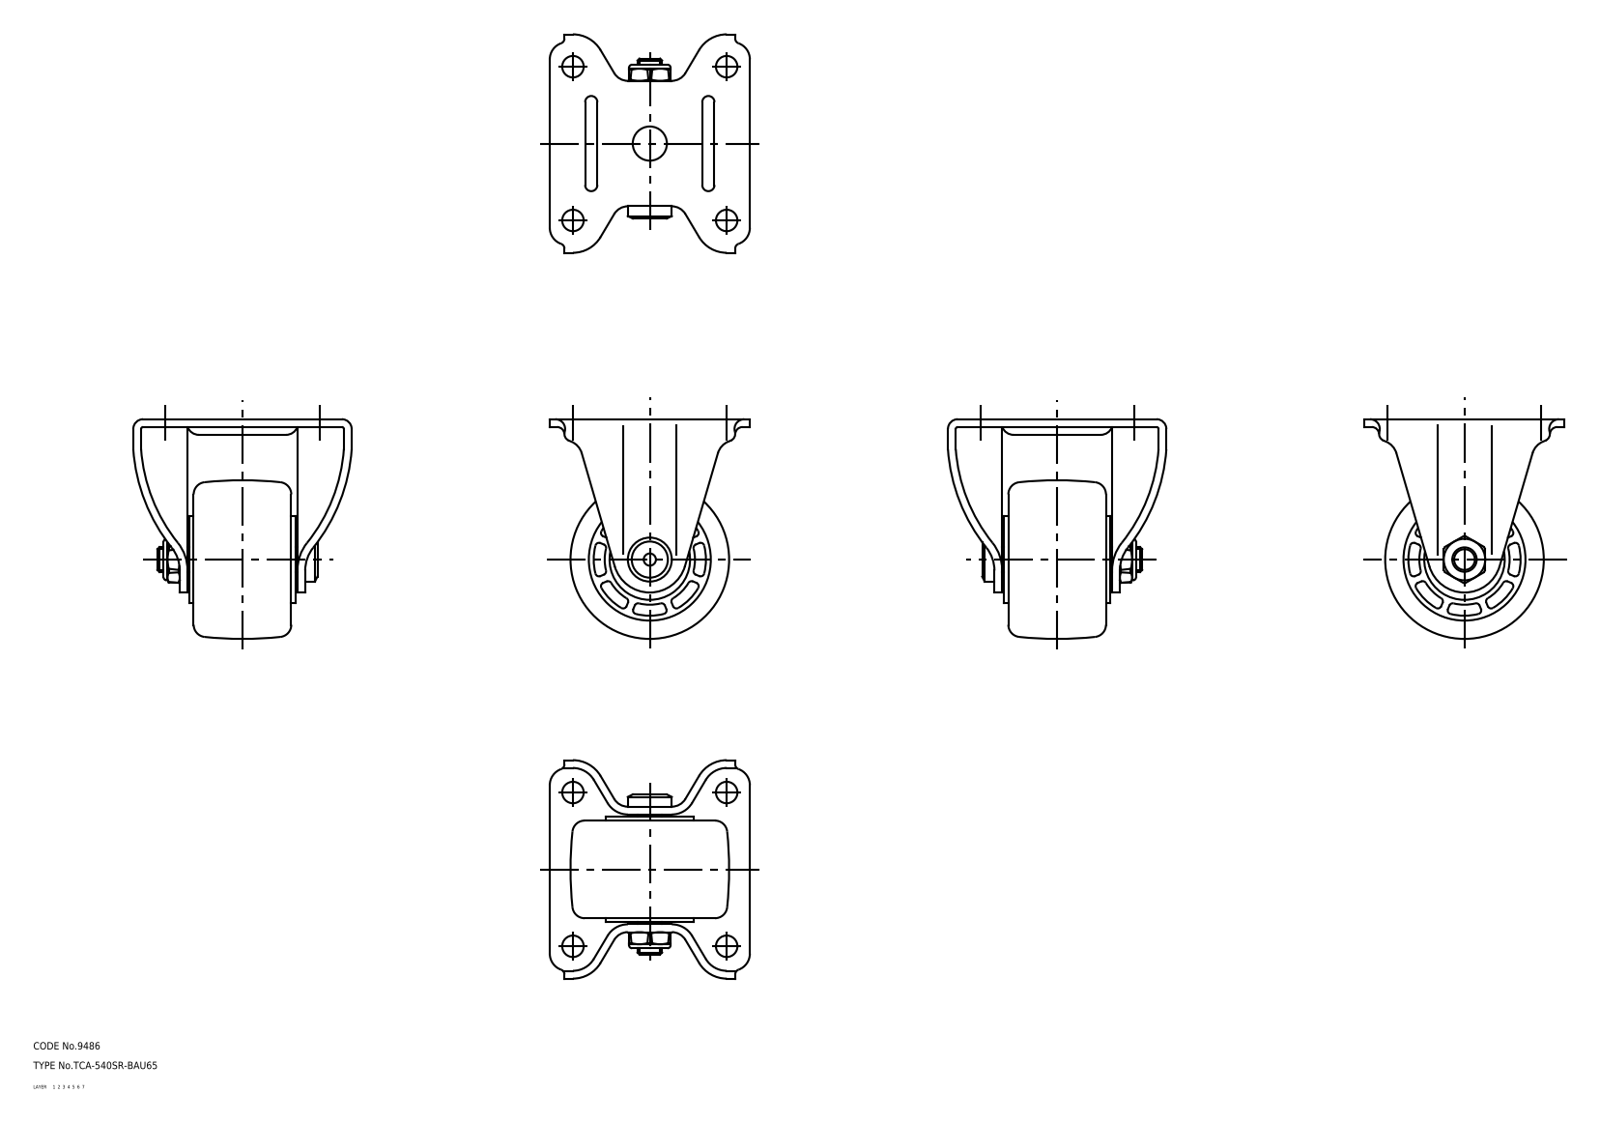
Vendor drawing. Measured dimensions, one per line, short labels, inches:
name: wheel; axle; No_540SR_BAU65_1063_36
written by: CADfix (AUTOMOTIVE_DESIGN)
unit: in
bodies: 3 solids, 303 faces (0 planar, 0 cylindrical, 303 other)
size: 3.543 × 3.524 × 3.228
volume: 9.466 in³; area: 86.34 in²
